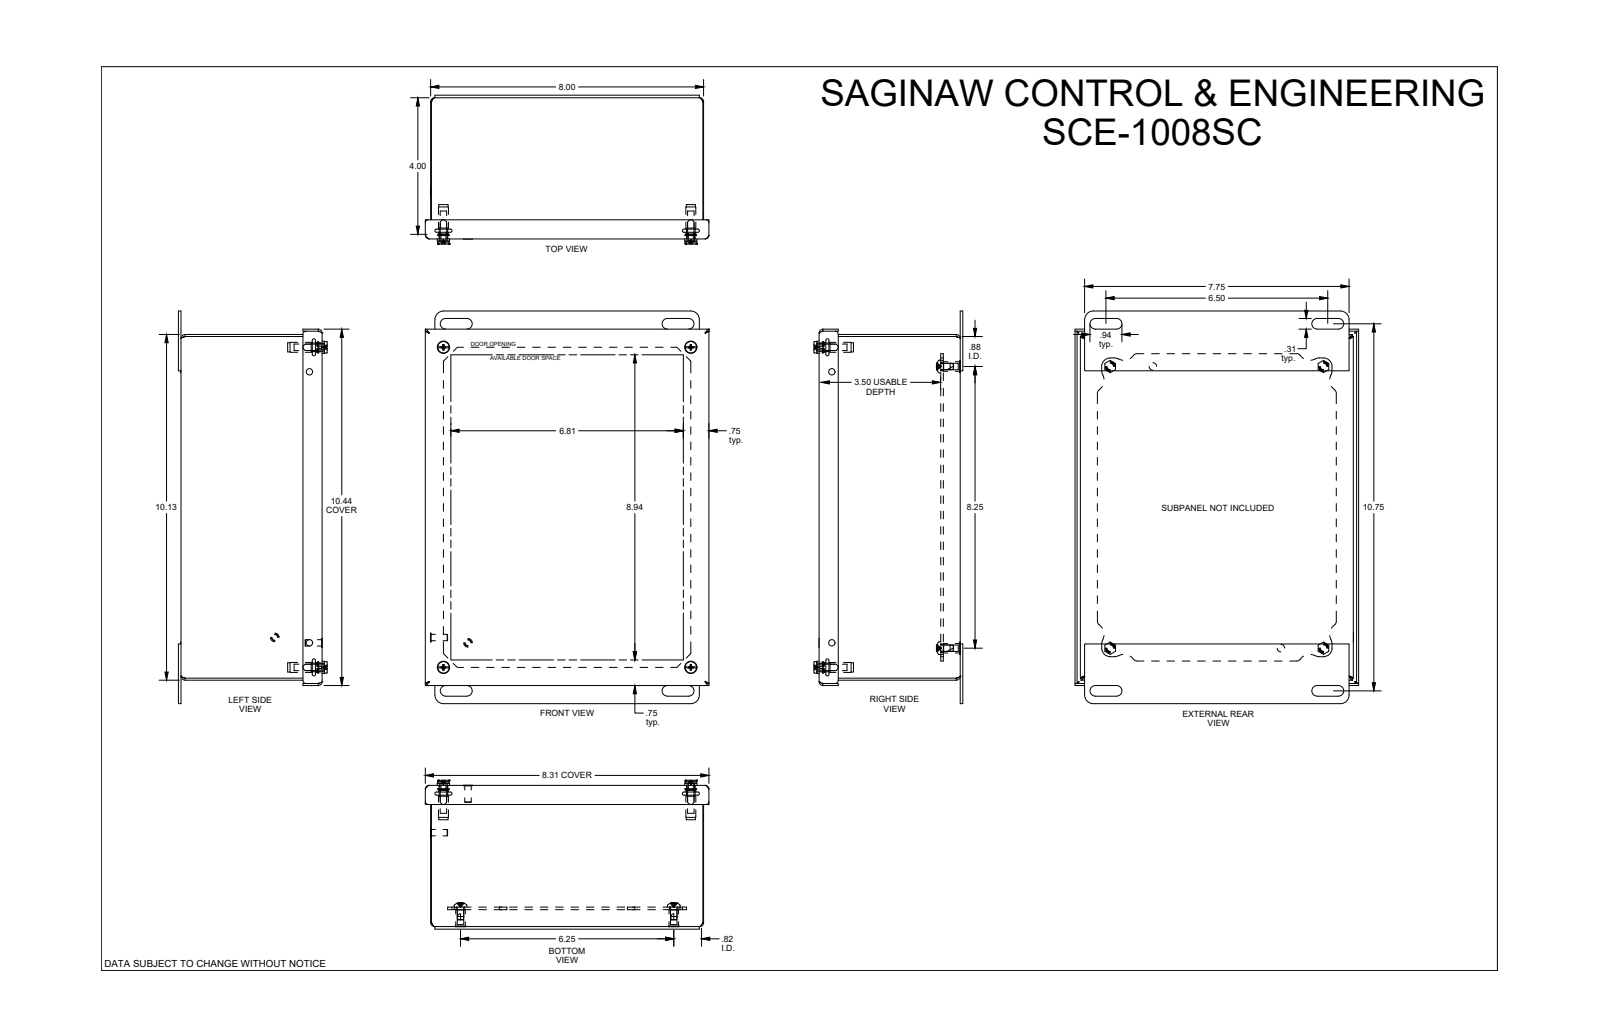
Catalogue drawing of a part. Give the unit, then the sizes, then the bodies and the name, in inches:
Units: inches
Overall size (bounding box): 11.5 × 8.313 × 4.361
Round holes (diameter × count): ⌀0.19 ×8, ⌀0.25 ×8, ⌀0.22 ×4, ⌀0.266 ×4, ⌀0.281 ×4, ⌀0.317 ×4, ⌀0.187 ×2, ⌀0.218 ×2, ⌀0.193 ×1
Round bosses / shafts (diameter × count): ⌀0.188 ×10, ⌀0.437 ×4, ⌀0.373 ×4, ⌀0.362 ×4, ⌀0.34 ×4, ⌀0.334 ×4, ⌀0.292 ×4, ⌀0.28 ×4
Partial cylindrical surfaces — rounded edges, fillets, slot ends (radius × count): R0.125 ×16, R0.25 ×16, R0.06 ×12, R0.005 ×8, R0.05 ×8, R0.063 ×8, R0.156 ×8, R0.255 ×8
Main face-to-face distances: 0.06, 4.075, 4.135, 4.015, 7.94, 3.505, 0.075, 0.57, 0.51, 3.565
Hole centre spacings: 8.827, 0.753, 11.101, 6.773, 8.25, 9.375, 10.35, 11.852
Volume: 28.1 in³ · Surface area: 900.6 in²
Bodies: 28 solids, 805 faces (328 planar, 207 cylindrical, 270 other)
Part name (STEP PRODUCT): SCE-1008SC
STEP written by: SolidWorks 2019 (AUTOMOTIVE_DESIGN)
